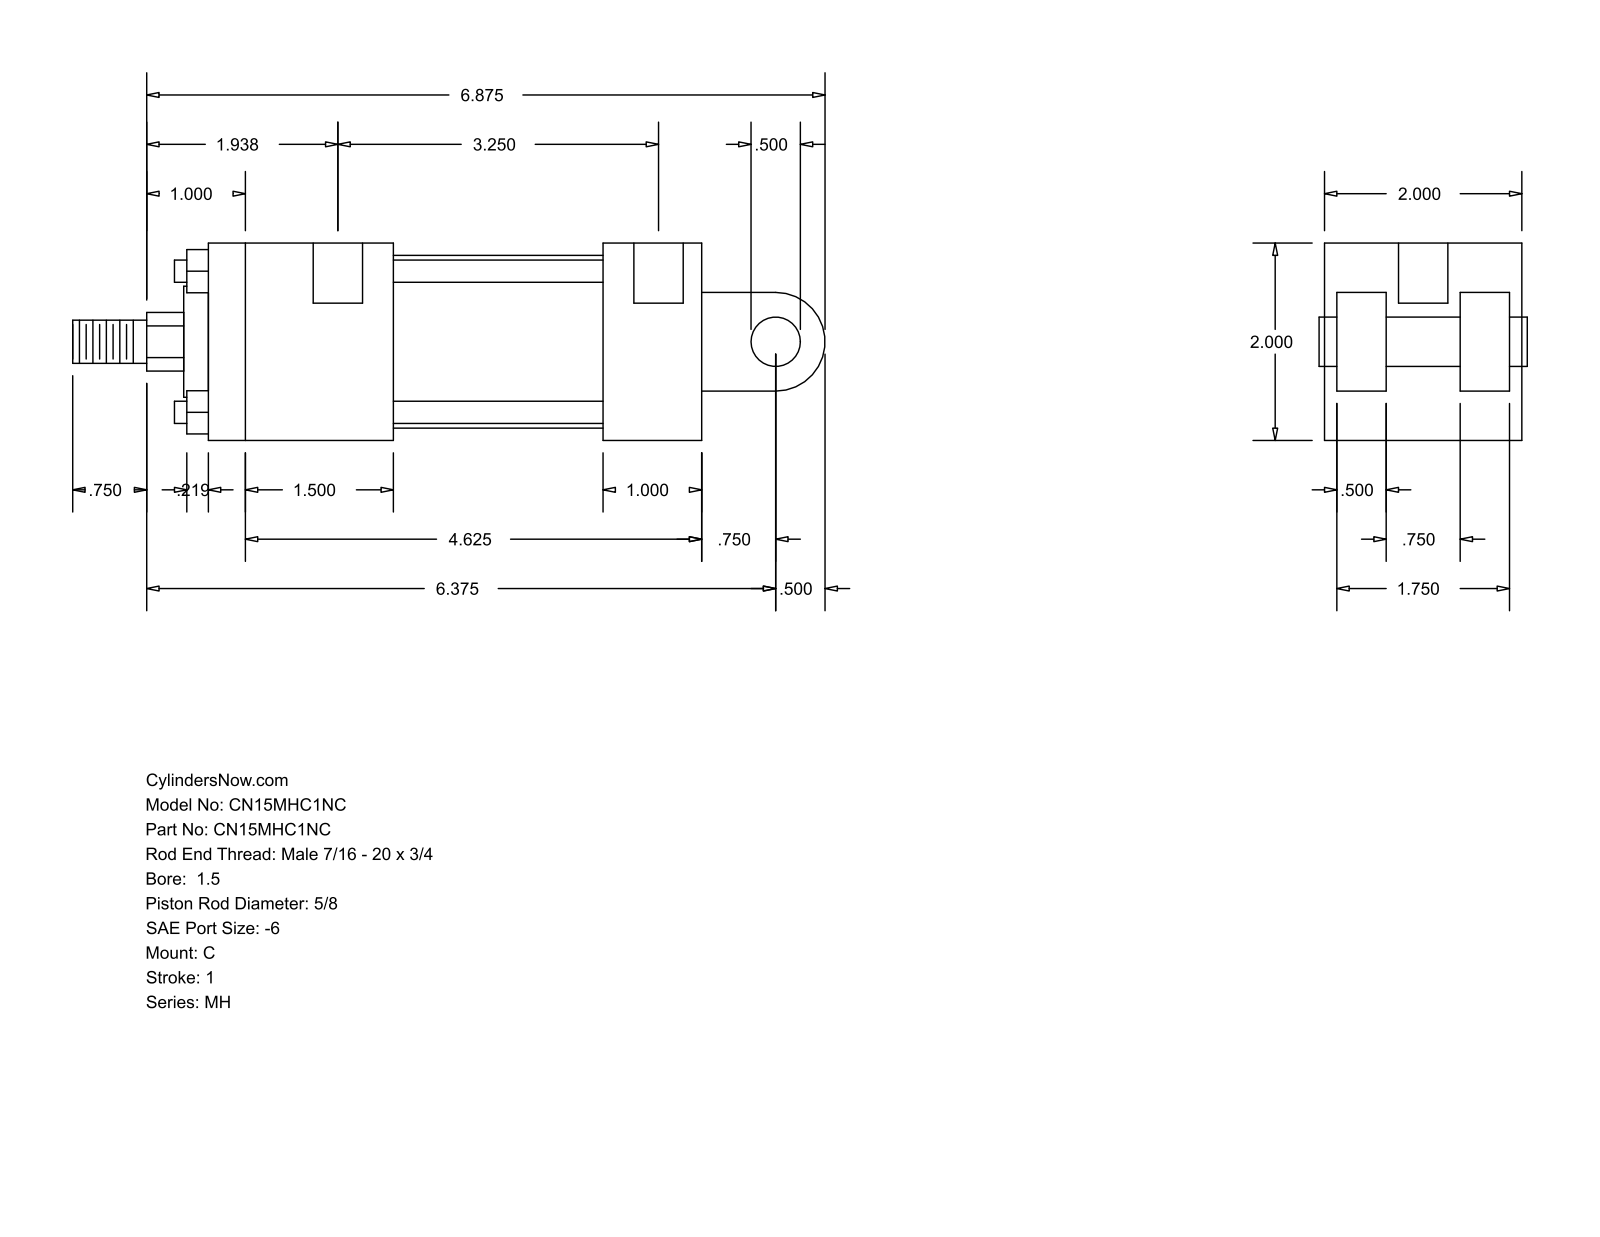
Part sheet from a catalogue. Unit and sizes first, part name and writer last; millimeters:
Units: millimetres
Overall size (bounding box): 193.68 × 50.8 × 50.8
Round holes (diameter × count): ⌀5.56 ×4, ⌀12.7 ×2
Round bosses / shafts (diameter × count): ⌀5.71 ×4, ⌀44.45 ×1, ⌀28.57 ×1, ⌀15.88 ×1, ⌀12.7 ×1, ⌀11.11 ×1
Partial cylindrical surfaces — rounded edges, fillets, slot ends (radius × count): R7.54 ×1, R12.7 ×1
Main face-to-face distances: 50.8, 12.7, 127, 53.97, 34.93, 3.17, 47.63, 15.87, 31.76, 38.1
Hole centre spacings: 85.72, 3.17, 82.55
Bodies: 0 solids, 99 faces (70 planar, 29 cylindrical, 0 other)
Part name (STEP PRODUCT): MH_C__0150_0.625
STEP written by: GSSL Pune (CONFIG_CONTROL_DESIGN)
